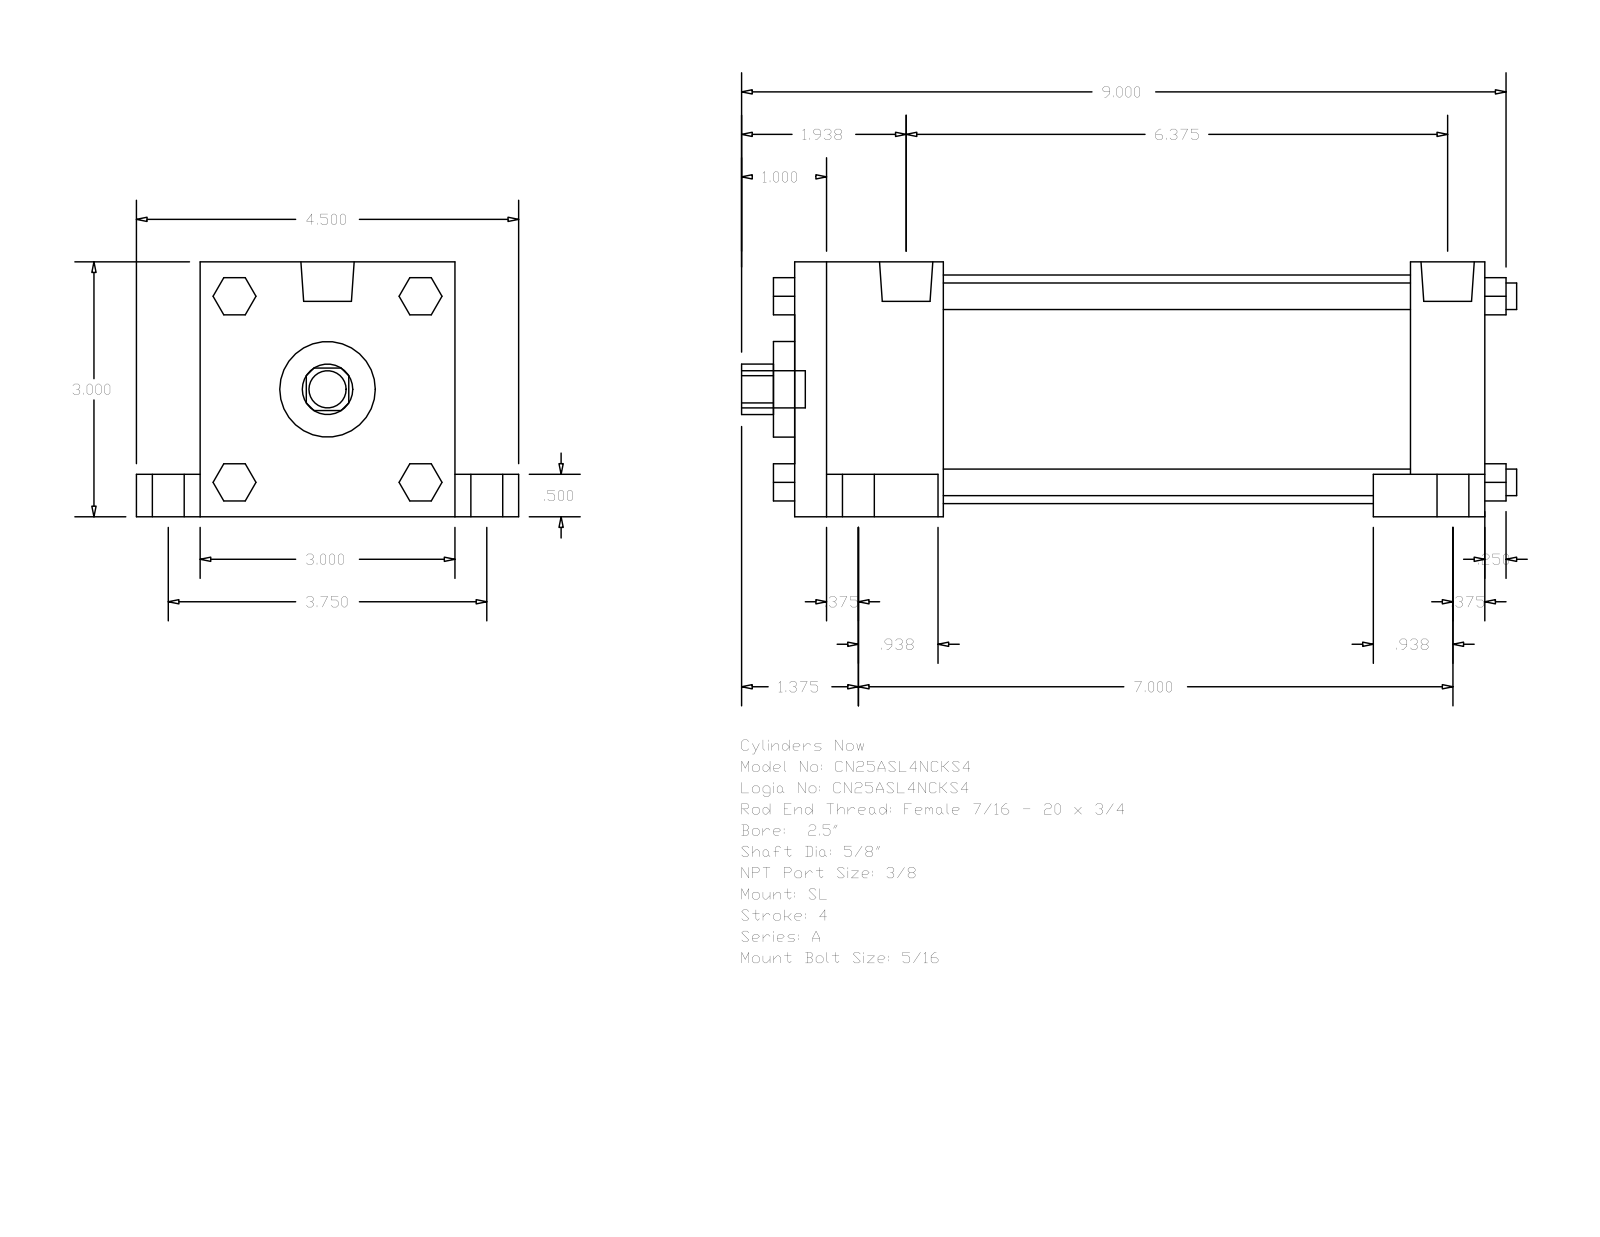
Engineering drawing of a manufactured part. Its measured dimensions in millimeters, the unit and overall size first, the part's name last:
Units: millimetres
Overall size (bounding box): 231.78 × 114.3 × 76.2
Round holes (diameter × count): ⌀15.88 ×1, ⌀28.57 ×1, ⌀68.33 ×1
Round bosses / shafts (diameter × count): ⌀15.88 ×4, ⌀9.53 ×4, ⌀7.94 ×4, ⌀5.56 ×4, ⌀15.93 ×2, ⌀11.11 ×1
Partial cylindrical surfaces — rounded edges, fillets, slot ends (radius × count): R7.54 ×1
Main face-to-face distances: 76.2, 206.37, 44.45, 22.22, 161.92, 184.15, 139.7, 12.7, 63.5, 19.05
Bodies: 0 solids, 148 faces (112 planar, 36 cylindrical, 0 other)
Part name (STEP PRODUCT): A_SL__0250_0.625
STEP written by: GSSL Pune (CONFIG_CONTROL_DESIGN)
